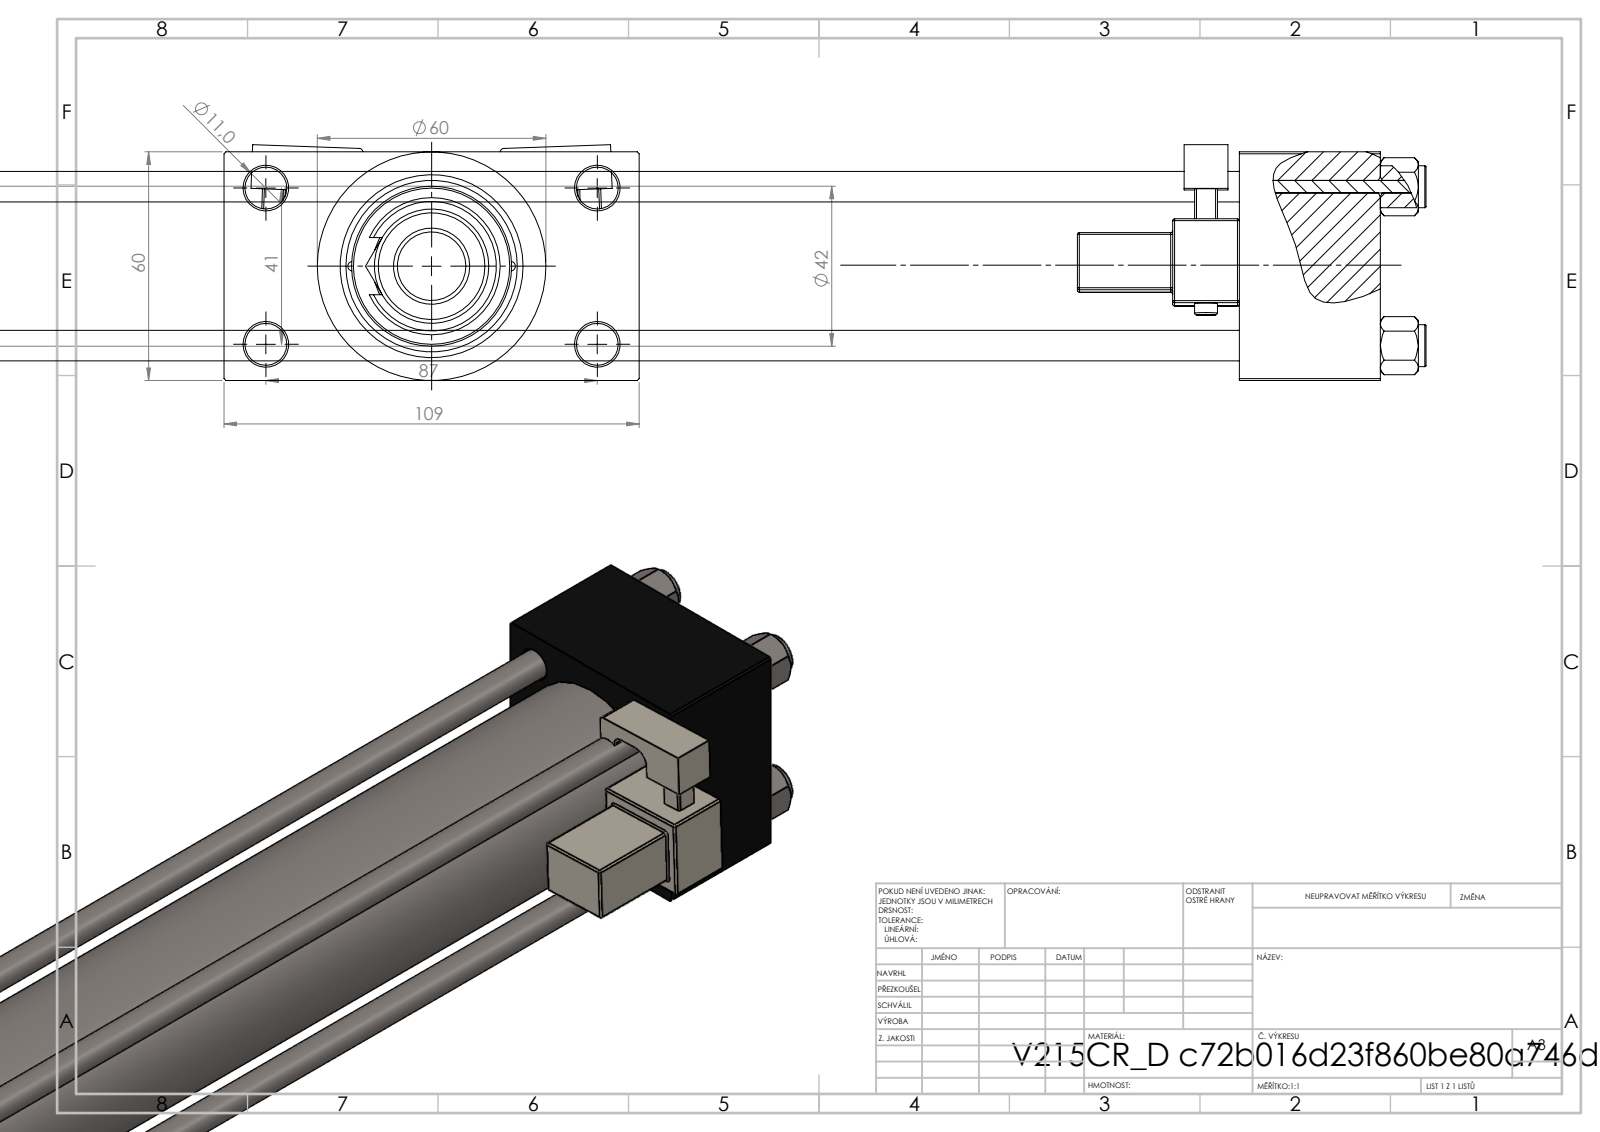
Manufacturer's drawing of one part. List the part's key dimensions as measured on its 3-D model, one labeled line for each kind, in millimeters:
Part name (STEP PRODUCT): V215CR_D_TYCINKA; V215CR_D_Body; V215CR_MSU; V215_VC_A (+4 more)
STEP written by: SolidWorks 2019 (CONFIG_CONTROL_DESIGN)
Units: millimetres
Bodies: 15 solids, 1353 faces (588 planar, 165 cylindrical, 600 other)
Overall size (bounding box): 599 × 109 × 61.9
Volume: 1 022 000 mm³ · Surface area: 305 767 mm²
Round holes (diameter × count): ⌀8 ×4, ⌀11 ×4, ⌀2.5 ×2, ⌀7 ×2, ⌀16.66 ×2, ⌀24 ×2, ⌀18.5 ×1, ⌀28 ×1, ⌀31 ×1, ⌀40 ×1, ⌀45 ×1
Round bosses / shafts (diameter × count): ⌀11 ×4, ⌀6 ×2, ⌀60 ×1, ⌀46 ×1, ⌀42 ×1, ⌀36 ×1, ⌀30 ×1, ⌀22 ×1
Partial cylindrical surfaces — rounded edges, fillets, slot ends (radius × count): R0.5 ×48, R1 ×2, R2.5 ×2, R4 ×2, R7.5 ×1, R12 ×1, R13.5 ×1
Main face-to-face distances: 60, 388, 24.5, 84.5, 37, 425, 43, 468, 431, 109
Hole centre spacings: 20.85, 22.65, 29.49, 30.62, 41.7, 46.53, 47.15, 48.09
